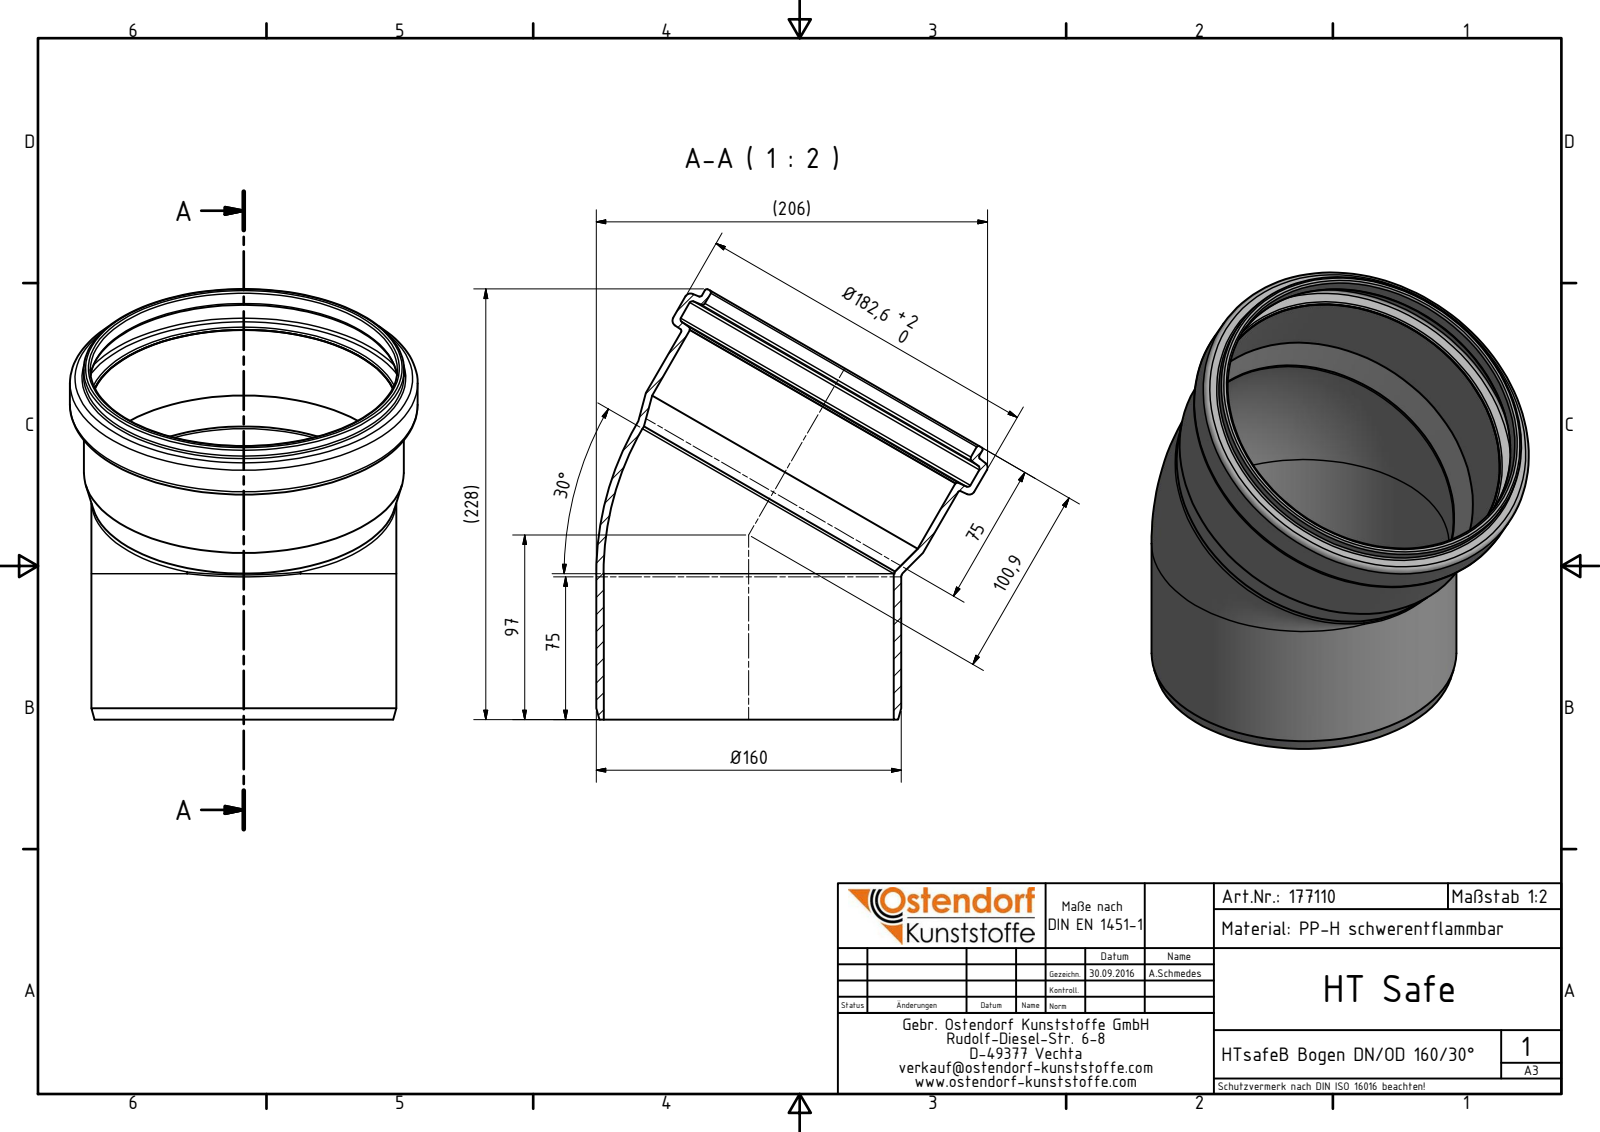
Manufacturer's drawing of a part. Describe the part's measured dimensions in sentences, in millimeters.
The part is named "177110 HTsafeB DN_OD 160_30°". Its 3-D file was written by "Autodesk Inventor 2016 (AUTOMOTIVE_DESIGN)". It is 1 solid with 35 faces: 4 planar, 11 cylindrical and 20 other. Overall it measures 226.09 by 205.47 by 182.6 millimeters. Its volume is 369 070 cubic millimeters and its surface area 213 260 square millimeters. Round holes: 2 of diameter 152.32, 1 of diameter 161, 1 of diameter 161.3, 1 of diameter 175.6. Round bosses or shafts: 2 of diameter 160.1, 1 of diameter 182.6, 1 of diameter 168.3, 1 of diameter 168. The main face-to-face distances are 23.21, 55.92, 79.13.
